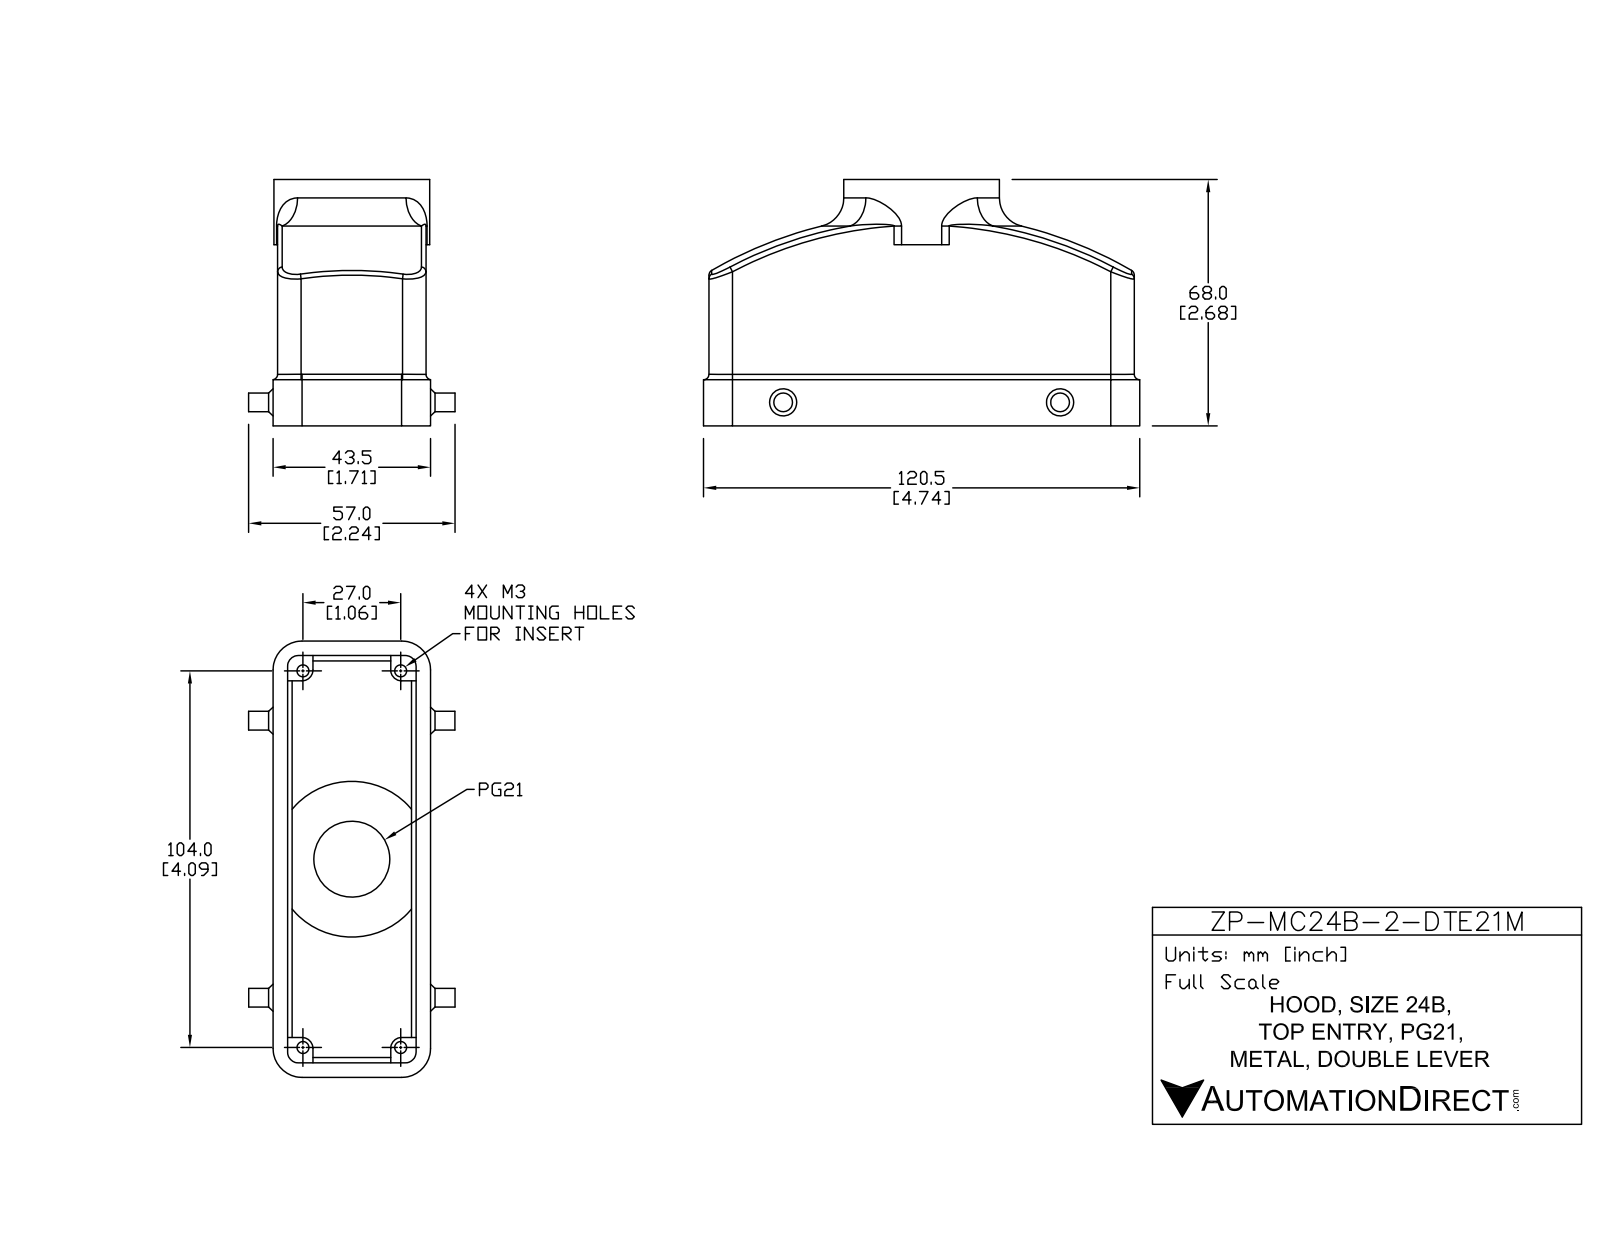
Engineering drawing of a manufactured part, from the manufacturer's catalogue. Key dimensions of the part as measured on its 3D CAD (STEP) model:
Part name (STEP PRODUCT): ZP-MC24B-2-DTE21M
STEP written by: SolidWorks 2011 (AUTOMOTIVE_DESIGN)
Units: millimetres
Bodies: 5 solids, 119 faces (46 planar, 41 cylindrical, 32 other)
Overall size (bounding box): 120.5 × 68 × 56
Volume: 90 081 mm³ · Surface area: 41 983 mm²
Round holes (diameter × count): ⌀3.3 ×4, ⌀21 ×1, ⌀27 ×1
Round bosses / shafts (diameter × count): ⌀5.17 ×2, ⌀43 ×1
Partial cylindrical surfaces — rounded edges, fillets, slot ends (radius × count): R3 ×8, R8 ×8, R1.5 ×4, R5.5 ×4, R6.5 ×4
Main face-to-face distances: 4, 37, 1.25, 38.25, 41, 33, 5.25, 42.25, 39.5, 2.75
Hole centre spacings: 53.72, 27, 104, 107.45
